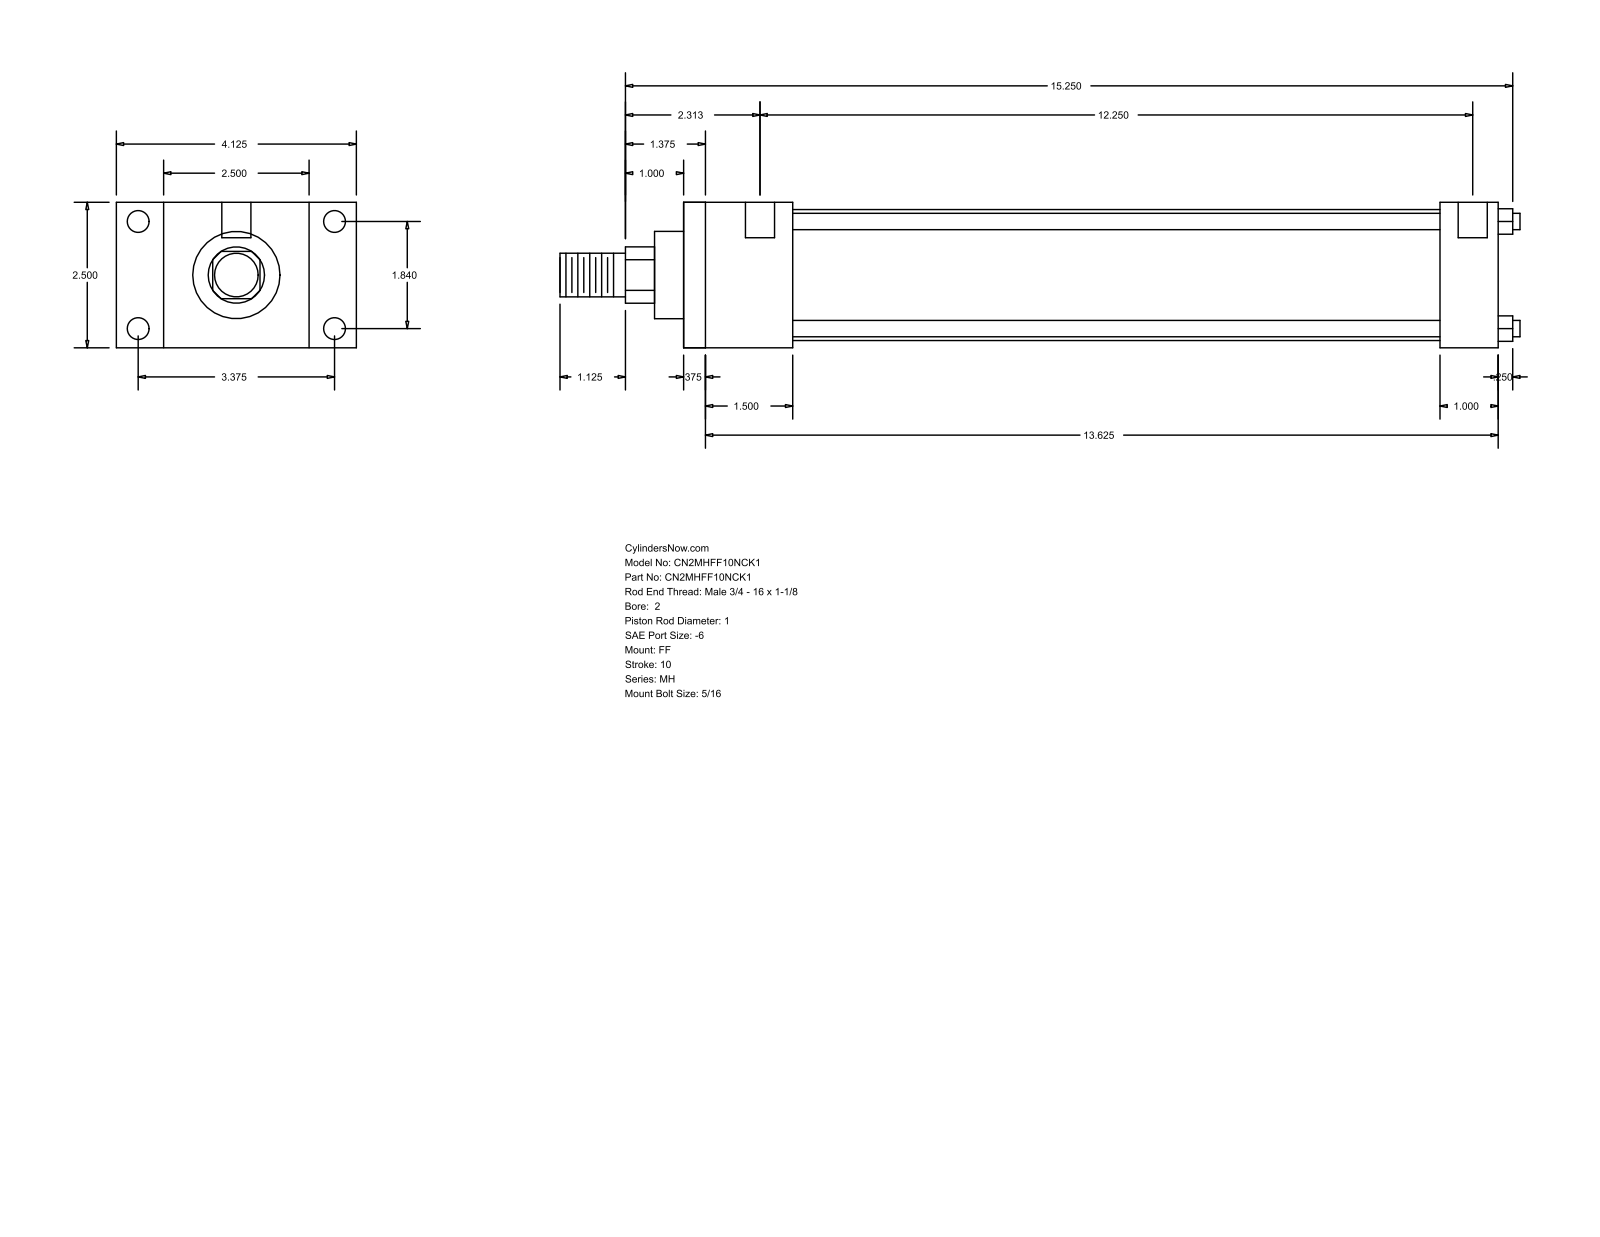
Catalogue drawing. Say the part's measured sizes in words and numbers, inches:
The part is named "MH_FF__0200_1". Its 3-D file was written by "GSSL Pune (CONFIG_CONTROL_DESIGN)". It is 0 solids with 92 faces: 64 planar, 28 cylindrical and 0 other. Overall it measures 16.5 by 4.125 by 2.5 inches. Round holes: 4 of diameter 0.219, 4 of diameter 0.375, 2 of diameter 0.5. Round bosses or shafts: 4 of diameter 0.281, 1 of diameter 2.25, 1 of diameter 1.5, 1 of diameter 1, 1 of diameter 0.75. Partial cylindrical surfaces (rounded edges, fillets, slot ends): 1 of radius 0.484. The main face-to-face distances are 2.5, 14, 0.375, 13.625, 0.813, 1, 1.875, 13, 1.5, 12.625. The hole center spacings are 1.84, 3.375, 3.844, 12.562, 0.125, 0.187, 12.25, 12.375.
